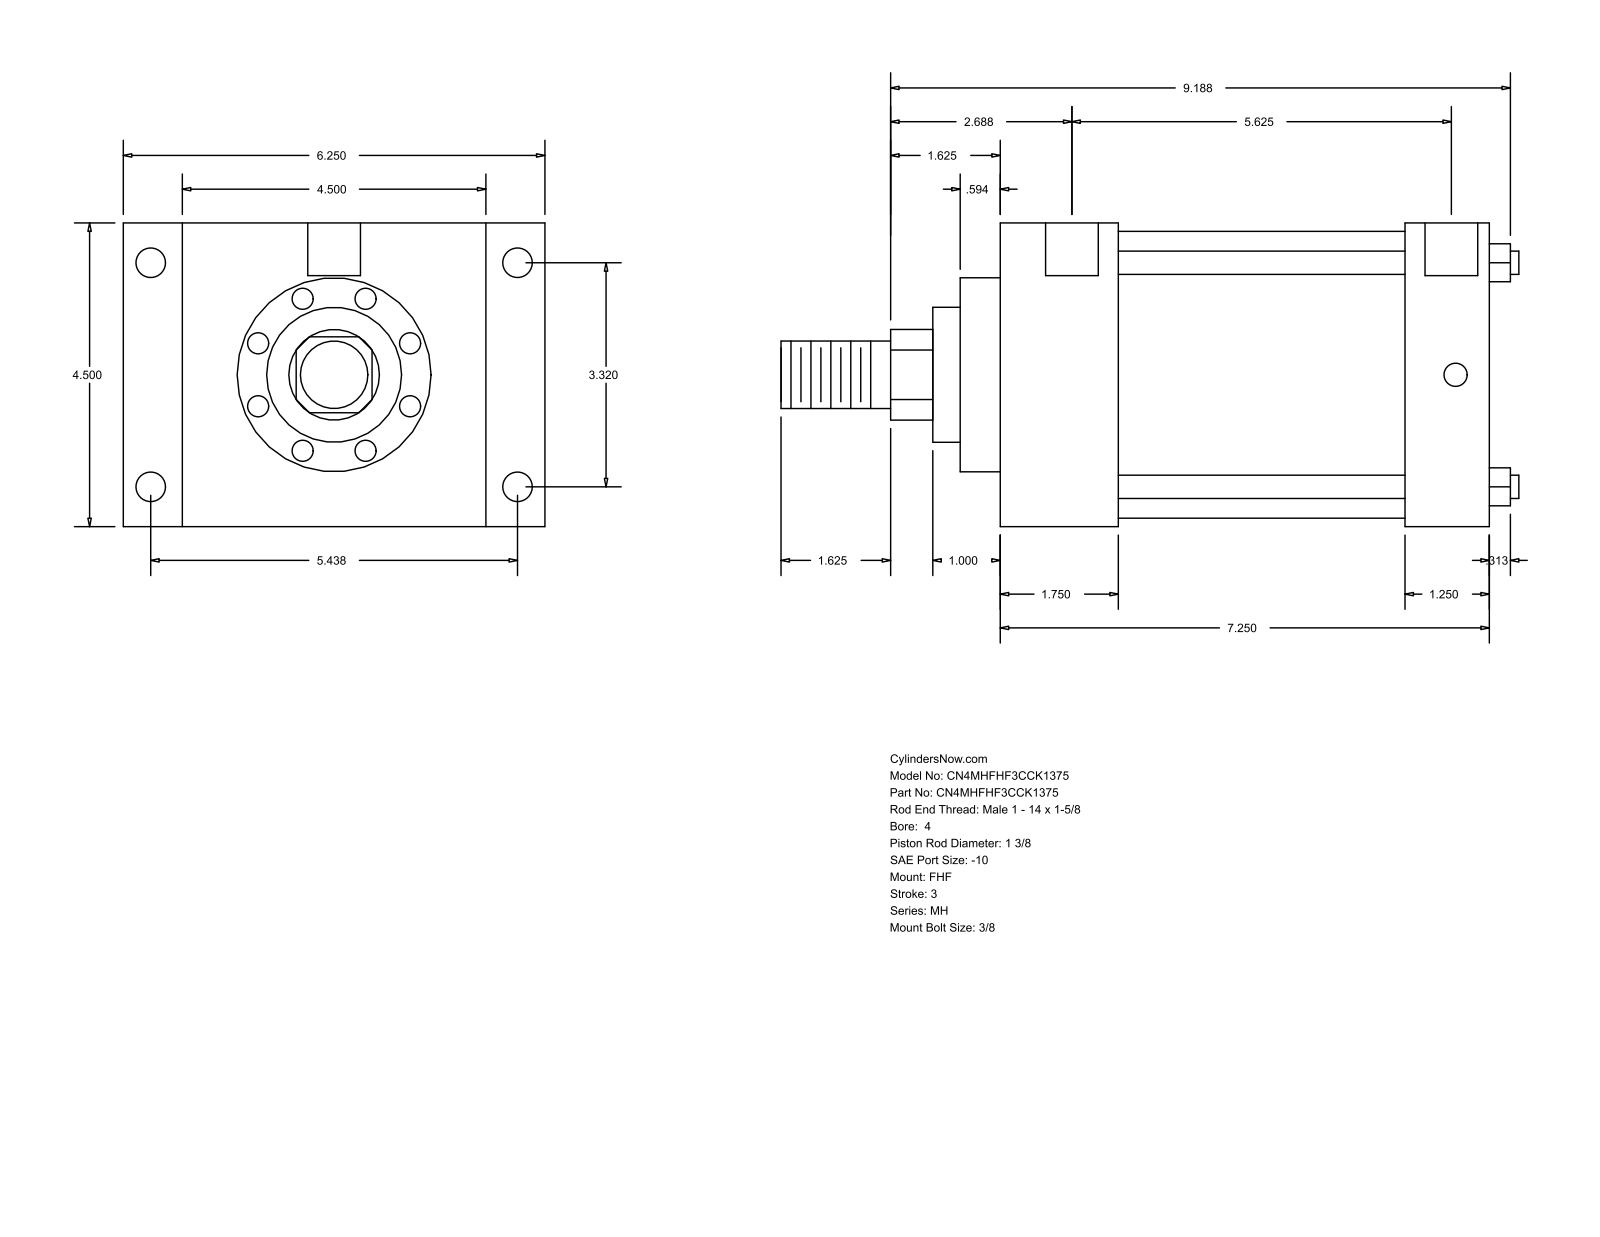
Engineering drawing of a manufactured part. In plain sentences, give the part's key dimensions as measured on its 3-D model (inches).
The part is named "MH_FHF__0400_1.375". Its 3-D file was written by "GSSL Pune (CONFIG_CONTROL_DESIGN)". It is 0 solids with 90 faces: 61 planar, 29 cylindrical and 0 other. Overall it measures 10.937 by 6.25 by 4.5 inches. Round holes: 4 of diameter 0.344, 4 of diameter 0.438, 2 of diameter 0.781. Round bosses or shafts: 4 of diameter 0.345, 1 of diameter 4.25, 1 of diameter 2.875, 1 of diameter 2, 1 of diameter 1.375, 1 of diameter 1. Partial cylindrical surfaces (rounded edges, fillets, slot ends): 1 of radius 0.672. The main face-to-face distances are 4.5, 7.25, 1.75, 5.5, 0.875, 5.375, 6.25, 6, 4.25, 1.25. The hole center spacings are 3.32, 5.438, 5.75, 6.371, 0.062, 0.063, 5.625, 5.687.
